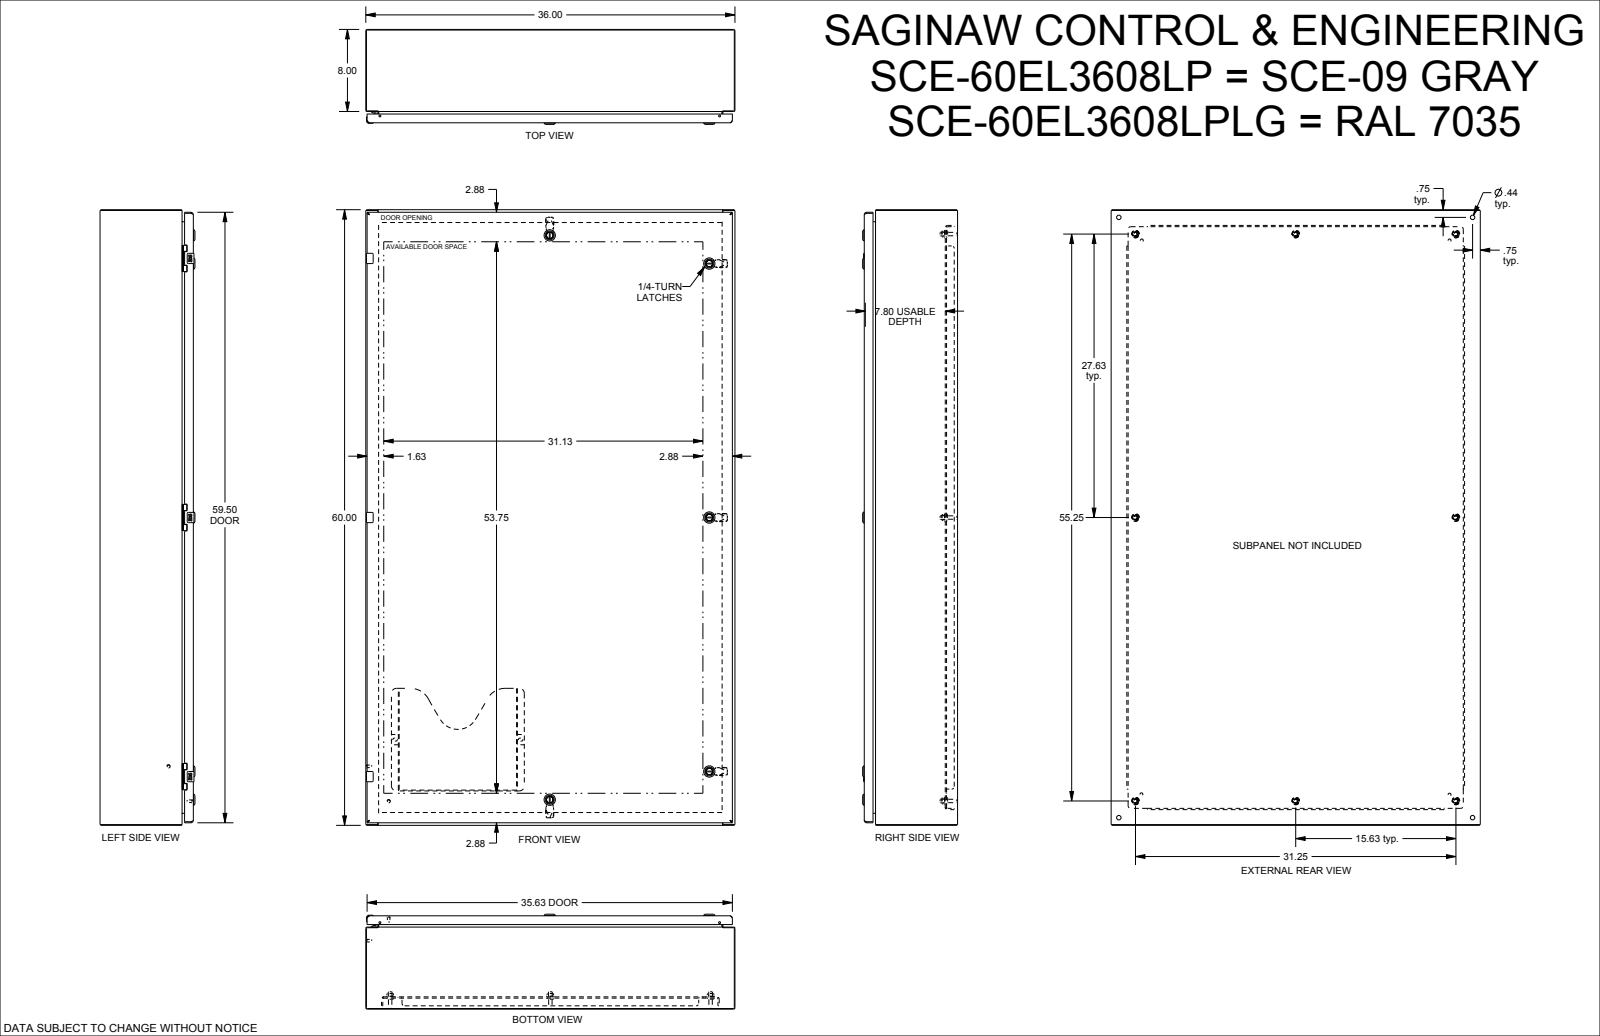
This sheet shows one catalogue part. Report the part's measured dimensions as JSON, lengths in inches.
{"part_name": "SCE-60EL3608LP_REV1", "step_written_by": "SolidWorks 2021 (AUTOMOTIVE_DESIGN)", "units": "inches", "bodies": {"solids": 35, "faces": 1788, "planar": 728, "cylindrical": 665, "other": 395}, "overall_size": [60, 36, 9.964], "volume_in3": 744.7, "surface_area_in2": 17417, "round_holes": [[0.5, 8], [0.197, 5], [0.394, 5], [0.634, 5], [0.281, 4], [0.437, 4], [0.156, 3], [0.188, 2], [0.274, 1]], "round_bosses_or_shafts": [[0.375, 8], [0.33, 8], [1.102, 5], [0.78, 5], [0.63, 5], [0.504, 5], [0.39, 5], [0.248, 4]], "partial_cylinders_radius": [[0.015, 28], [0.157, 20], [0.04, 17], [0.26, 16], [0.031, 12], [0.043, 12], [0.062, 12], [0.1, 12]], "face_to_face_distances": [0.075, 0.06, 9.097, 9.022, 9.037, 8.962, 1.125, 0.125, 1.075, 1], "hole_center_spacings": [2.298, 15.625, 17.327, 27.625, 29.296, 31.738, 32.916, 41.71]}
